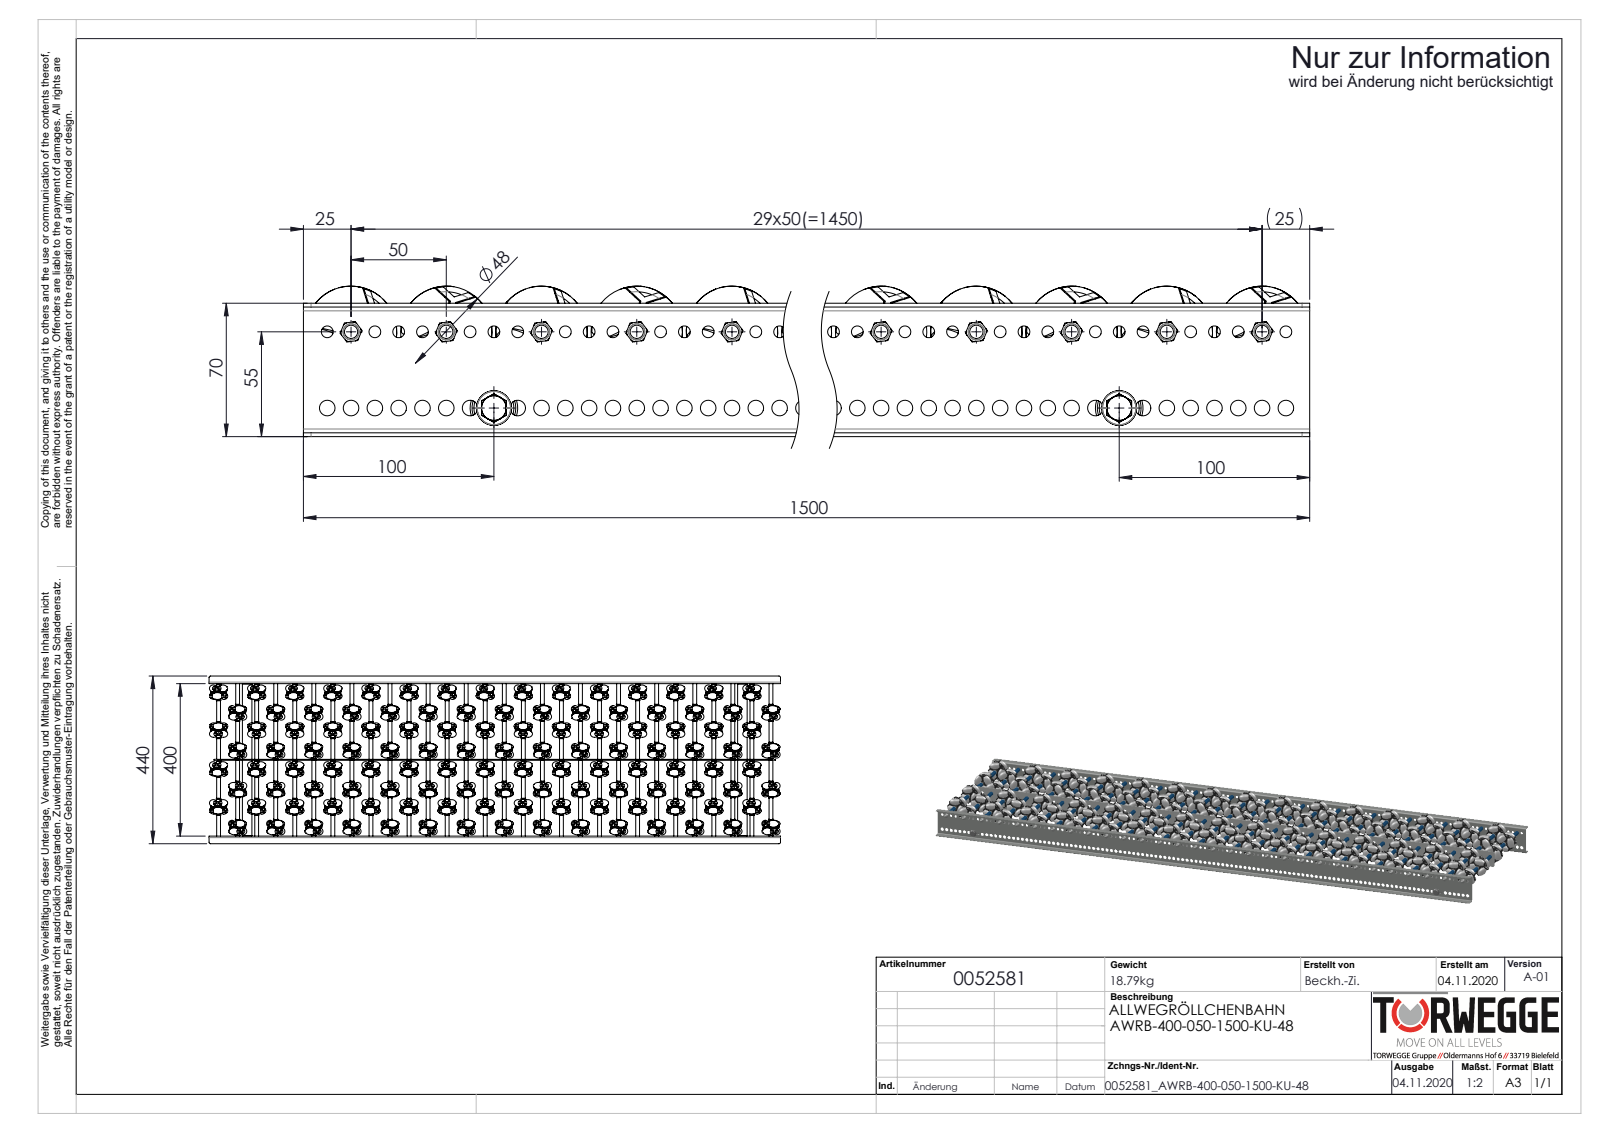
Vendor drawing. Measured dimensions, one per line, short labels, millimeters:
name: S108767_Längstraverse-42x2,5-AWR_L1500; AWR48_Stift; 0052581; 0015028_AWR48 (+8 more)
written by: SolidWorks 2020 (AUTOMOTIVE_DESIGN)
unit: mm
bodies: 2023 solids, 35980 faces (12426 planar, 13910 cylindrical, 9644 other)
size: 1500 × 440 × 79
volume: 6 651 000 mm³; area: 4 514 000 mm²
holes: 720× ⌀3.7, 720× ⌀4.2, 119× ⌀6.2, 119× ⌀8.2, 59× ⌀6.5, 30× ⌀4.92, 30× ⌀8.4, 2× ⌀6.8, 2× ⌀21
bosses: 720× ⌀4, 630× ⌀3.7, 32× ⌀8, 30× ⌀42, 30× ⌀11, 30× ⌀10, 30× ⌀7, 30× ⌀6
rounds: 30× R23.55, 8× R4, 4× R2, 4× R5
face distances: 2, 402, 68, 400, 404, 203.4, 200.6, 198.6, 201.4, 203.1
hole spacings: 36.06, 36.05, 36.07, 36.04, 4, 169.07, 8, 22.11
